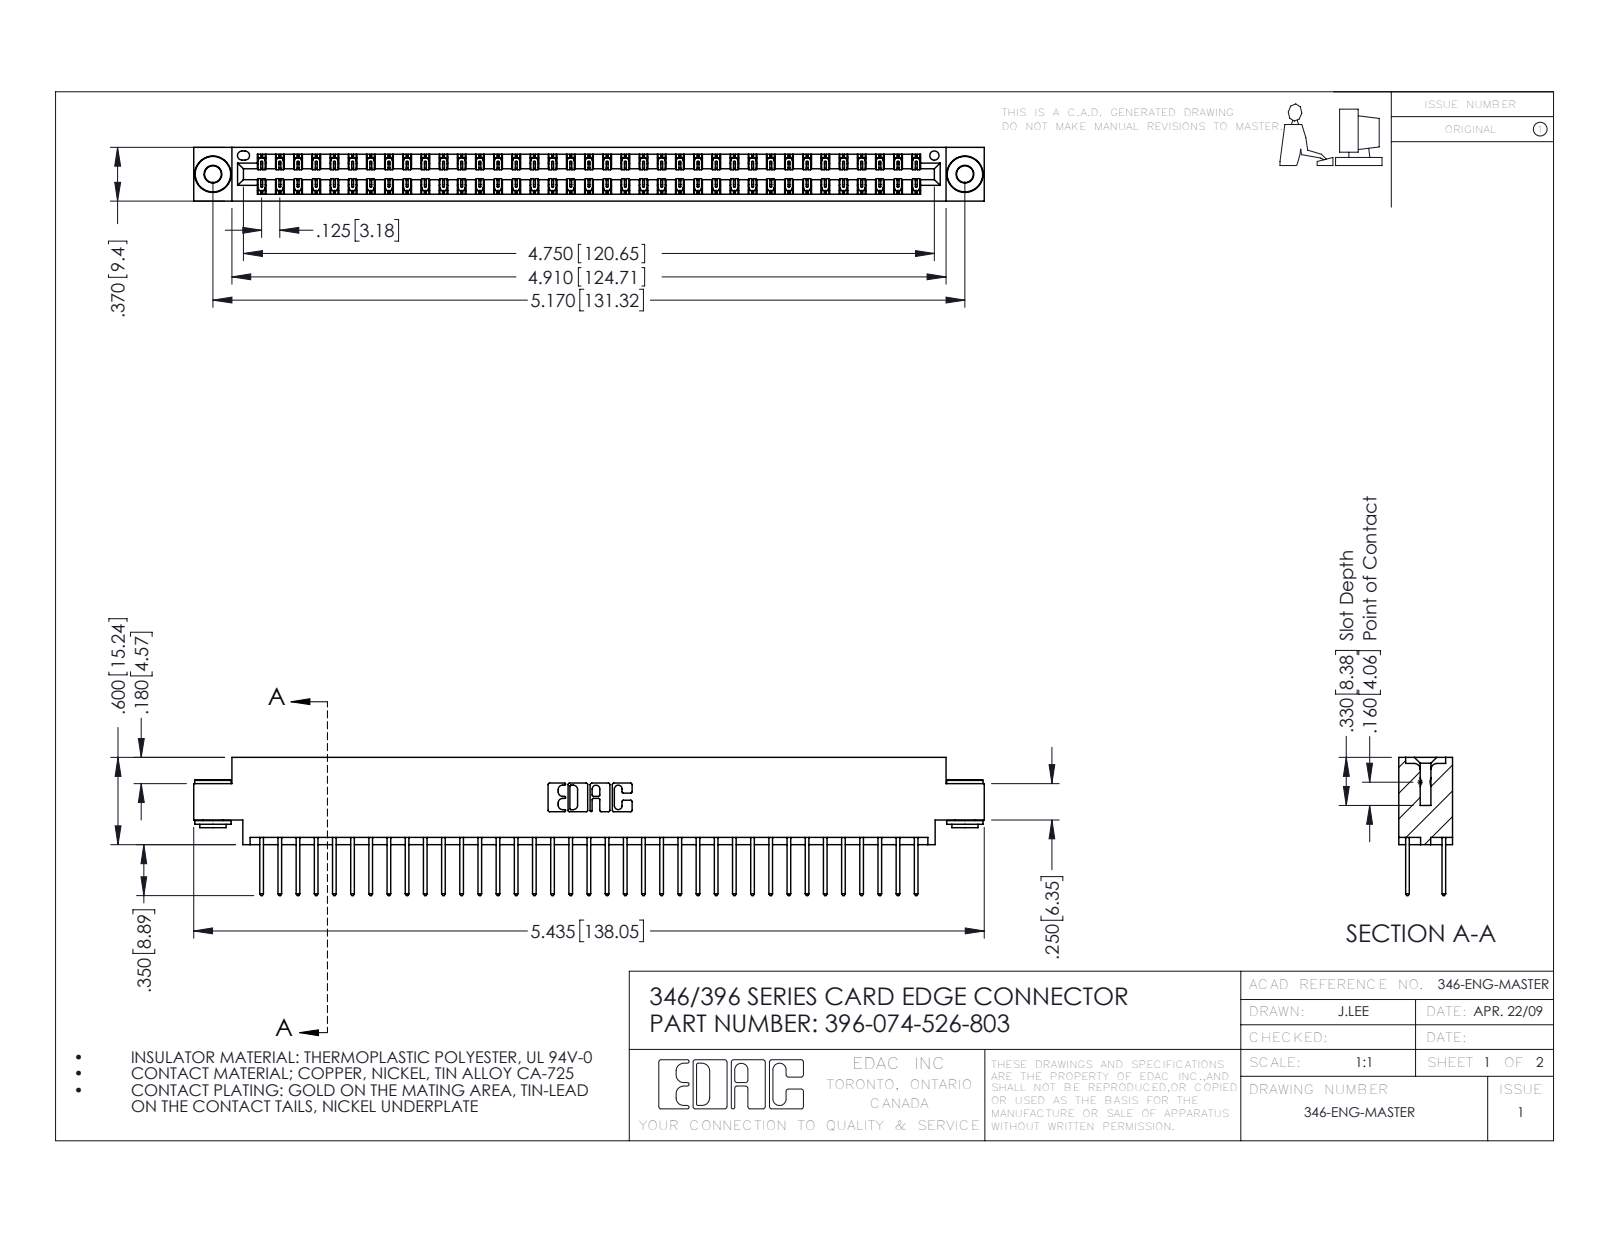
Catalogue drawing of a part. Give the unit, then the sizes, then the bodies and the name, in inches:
Units: inches
Overall size (bounding box): 5.435 × 0.95 × 0.37
Round holes (diameter × count): ⌀0.116 ×2, ⌀0.156 ×2, ⌀0.064 ×1
Round bosses / shafts (diameter × count): ⌀0.25 ×2, ⌀0.18 ×2, ⌀0.136 ×2
Partial cylindrical surfaces — rounded edges, fillets, slot ends (radius × count): R0.006 ×111, R0.01 ×74, R0.01 ×22, R0.007 ×6, R0.031 ×6, R0.026 ×3, R0.014 ×2, R0.022 ×2
Main face-to-face distances: 0.048, 0.322, 0.25, 0.37, 0.025, 0.072, 0.298, 0.275, 0.148, 0.222
Hole centre spacings: 0.246, 4.961, 5.17
Volume: 0.818 in³ · Surface area: 29.9 in²
Bodies: 77 solids, 4012 faces (2680 planar, 1324 cylindrical, 8 other)
Part name (STEP PRODUCT): 396-074-526-803; 346 Part_0.170 Offset - 0.156 Dia-TH; 345-250-002_345-250-002-102; 345-292-001_345-293-126
STEP written by: SolidWorks 2016 (CONFIG_CONTROL_DESIGN)
